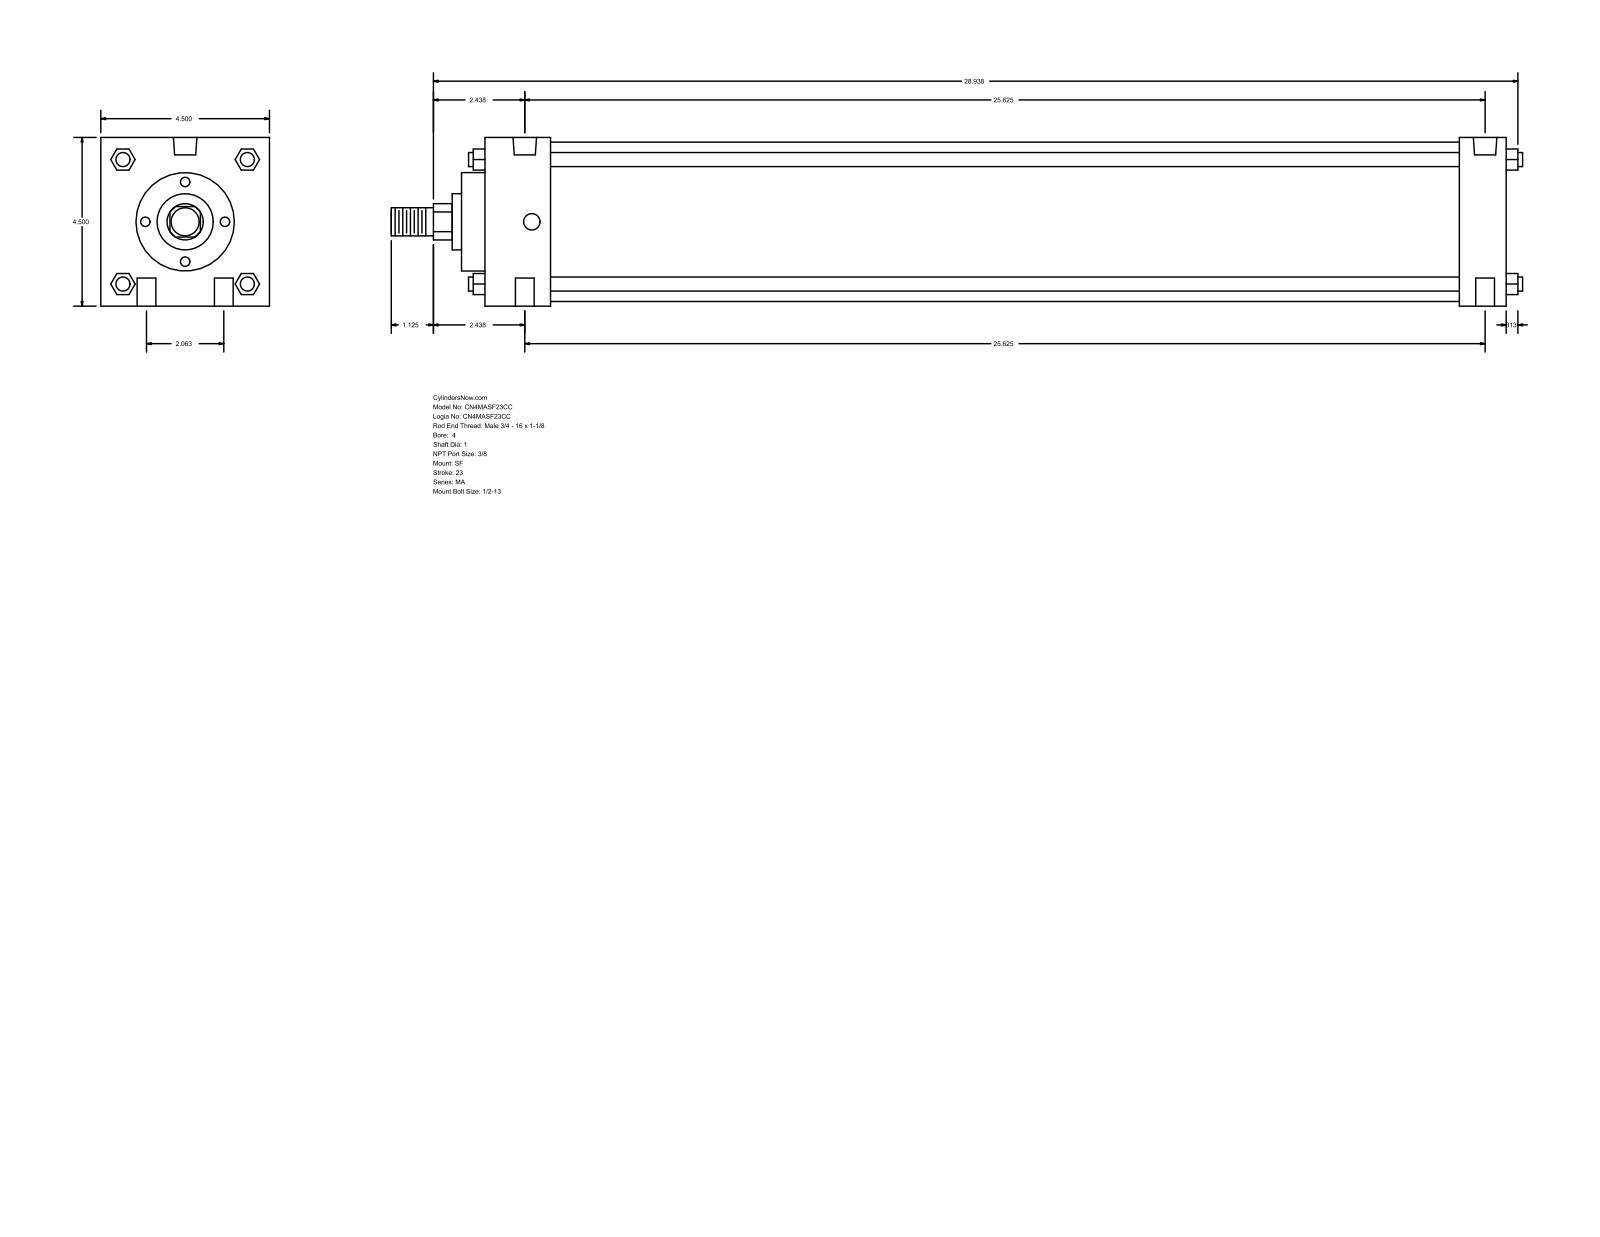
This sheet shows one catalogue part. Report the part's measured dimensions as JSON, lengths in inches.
{"part_name": "MA_SF__0400_1", "step_written_by": "GSSL Pune (CONFIG_CONTROL_DESIGN)", "units": "inches", "bodies": {"solids": 0, "faces": 126, "planar": 95, "cylindrical": 31, "other": 0}, "overall_size": [30.187, 4.5, 4.5], "round_holes": [[0.5, 4], [0.437, 2], [0.627, 2]], "round_bosses_or_shafts": [[0.375, 4], [4.25, 1], [2.625, 1], [1.5, 1], [1, 1], [0.75, 1]], "partial_cylinders_radius": [[0.484, 1]], "face_to_face_distances": [4.5, 27.25, 26, 1.25, 1.75, 24.25, 25.5, 0.625, 2.375, 26.625], "hole_center_spacings": [1.031, 25.646, 25.625, 2.062, 25.708, 25.25]}
